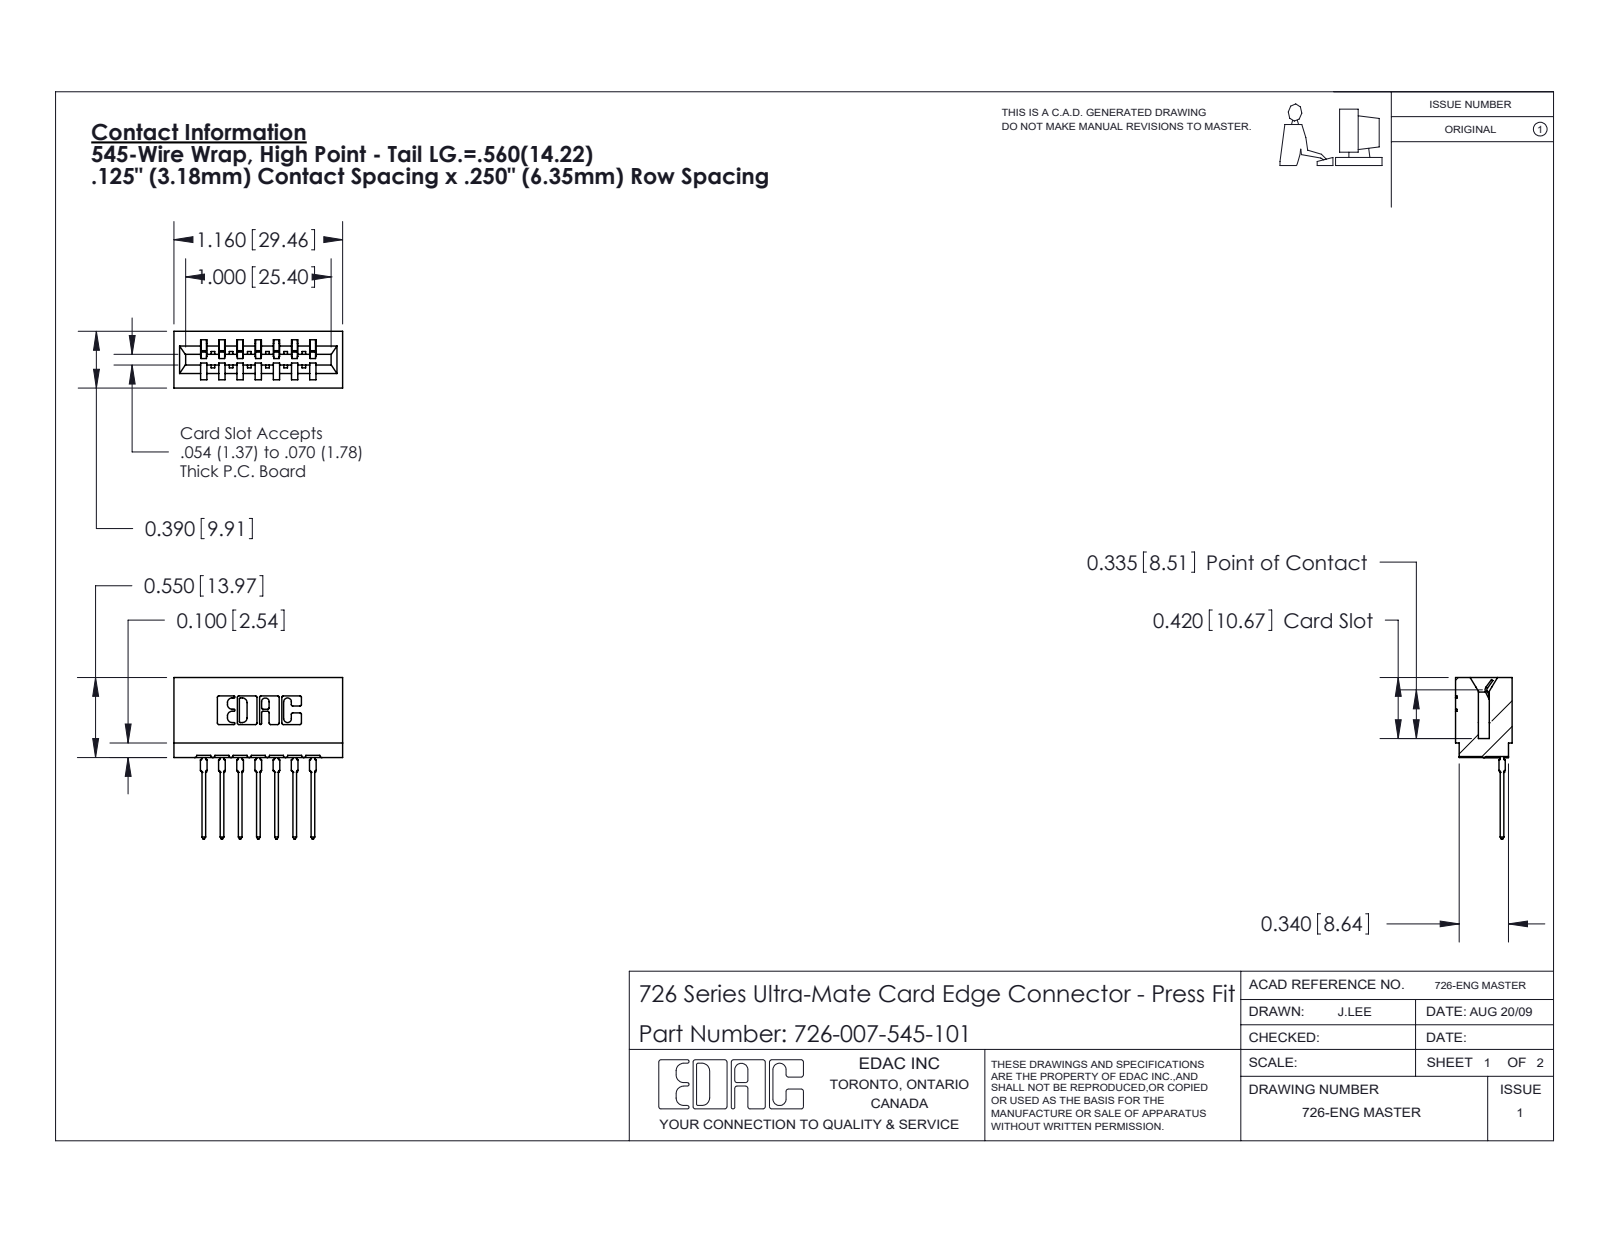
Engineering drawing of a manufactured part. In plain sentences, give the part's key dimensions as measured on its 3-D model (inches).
The part is named "726 Part_.515 Slot Depth - 01; 746-292-001_545; 726-007-545-101". Its 3-D file was written by "SolidWorks 2020 (CONFIG_CONTROL_DESIGN)". It is 8 solids with 853 faces: 496 planar, 175 cylindrical and 182 other. Overall it measures 1.16 by 1.109 by 0.39 inches. Its volume is 0.174 cubic inches and its surface area 6.097 square inches. Partial cylindrical surfaces (rounded edges, fillets, slot ends): 22 of radius 0.01, 14 of radius 0.021, 8 of radius 0.015, 6 of radius 0.007, 6 of radius 0.031, 4 of radius 0.005, 4 of radius 0.011, 3 of radius 0.026. The main face-to-face distances are 0.25, 0.333, 0.042, 0.057, 0.125, 0.125, 0.5, 0.292, 0.208, 0.083.
